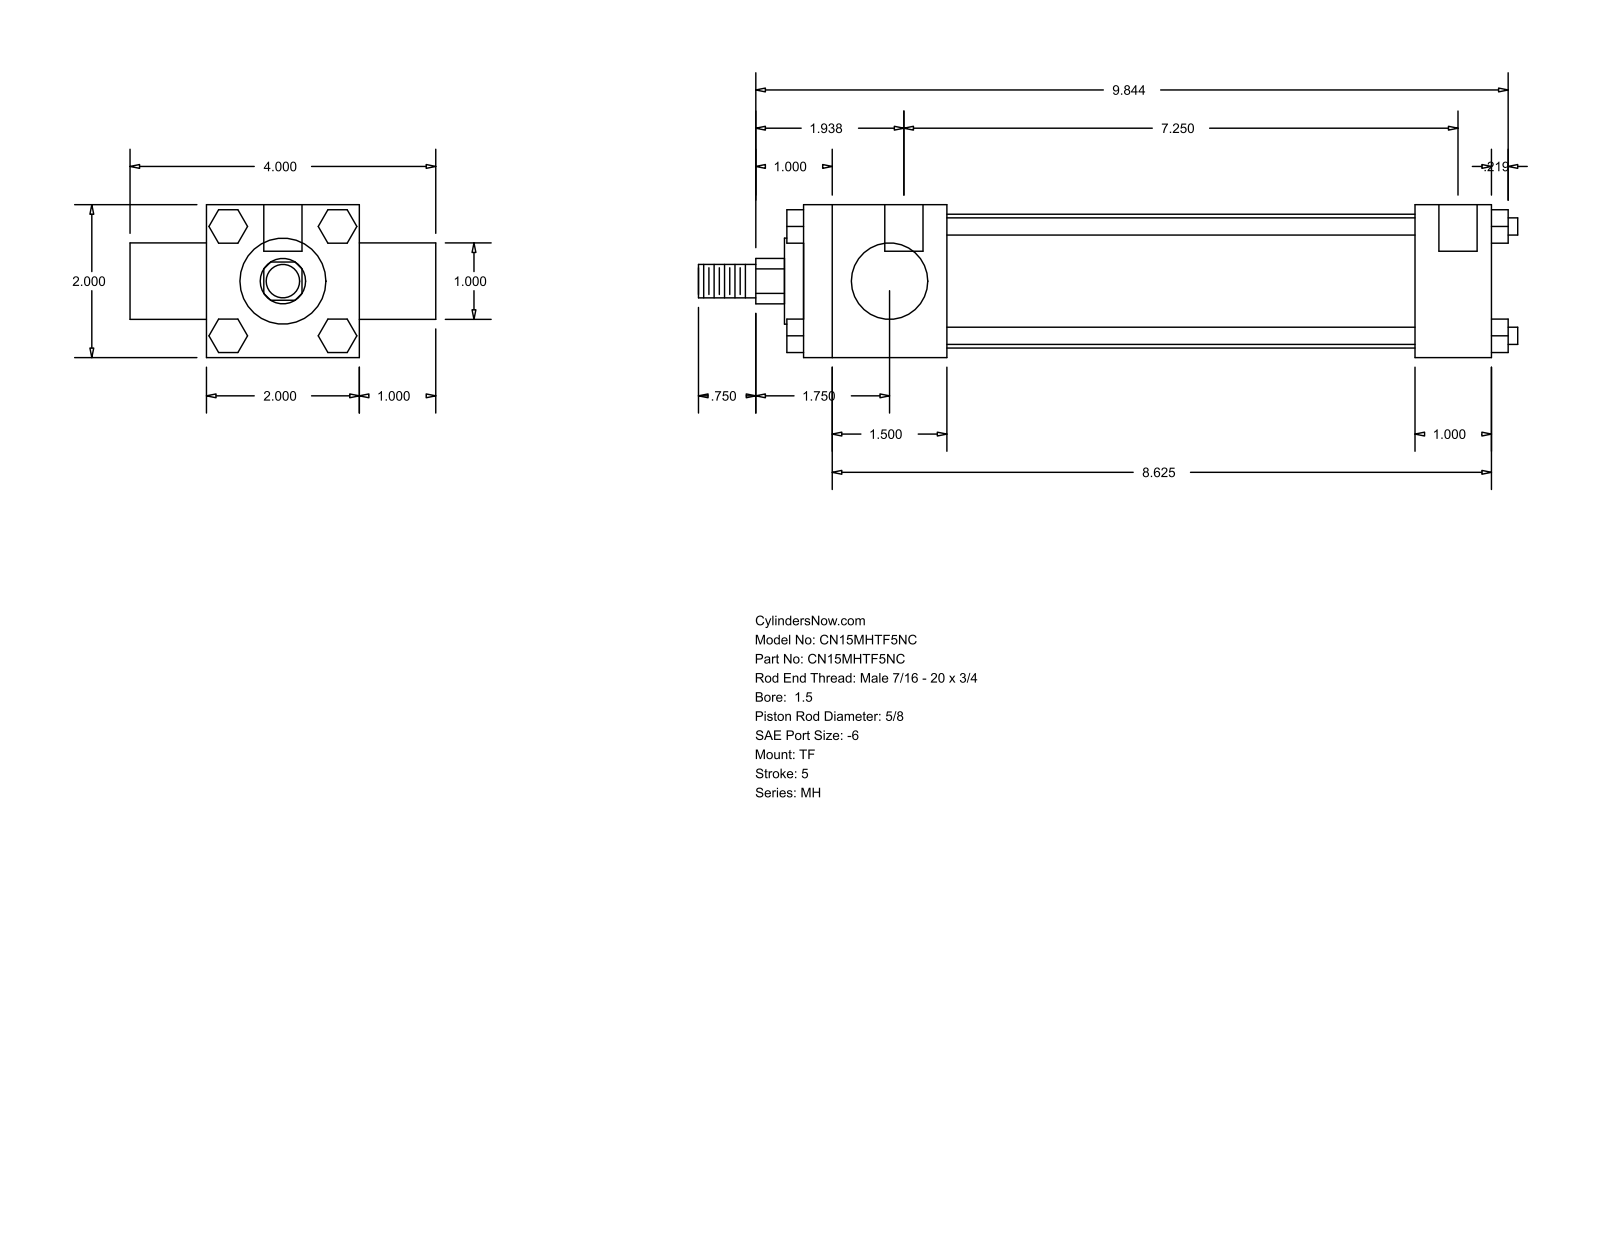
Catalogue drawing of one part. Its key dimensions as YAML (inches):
part_name: "MH_TF__0150_0.625"
step_written_by: "GSSL Pune (CONFIG_CONTROL_DESIGN)"
units: inches
bodies: {solids: 0, faces: 120, planar: 92, cylindrical: 28, other: 0}
overall_size: [10.719, 4, 2]
round_holes:
  - {diameter: 0.219, count: 3}
  - {diameter: 0.5, count: 2}
round_bosses_or_shafts:
  - {diameter: 0.225, count: 4}
  - {diameter: 1.75, count: 1}
  - {diameter: 1.125, count: 1}
  - {diameter: 1, count: 1}
  - {diameter: 0.625, count: 1}
  - {diameter: 0.437, count: 1}
partial_cylinders:
  - {radius: 0.297, count: 1}
face_to_face_distances: [2, 1, 9, 3, 1.875, 7.125, 8, 6.125, 0.219, 9.219]
hole_center_spacings: [0.125, 7.25, 7.375]
